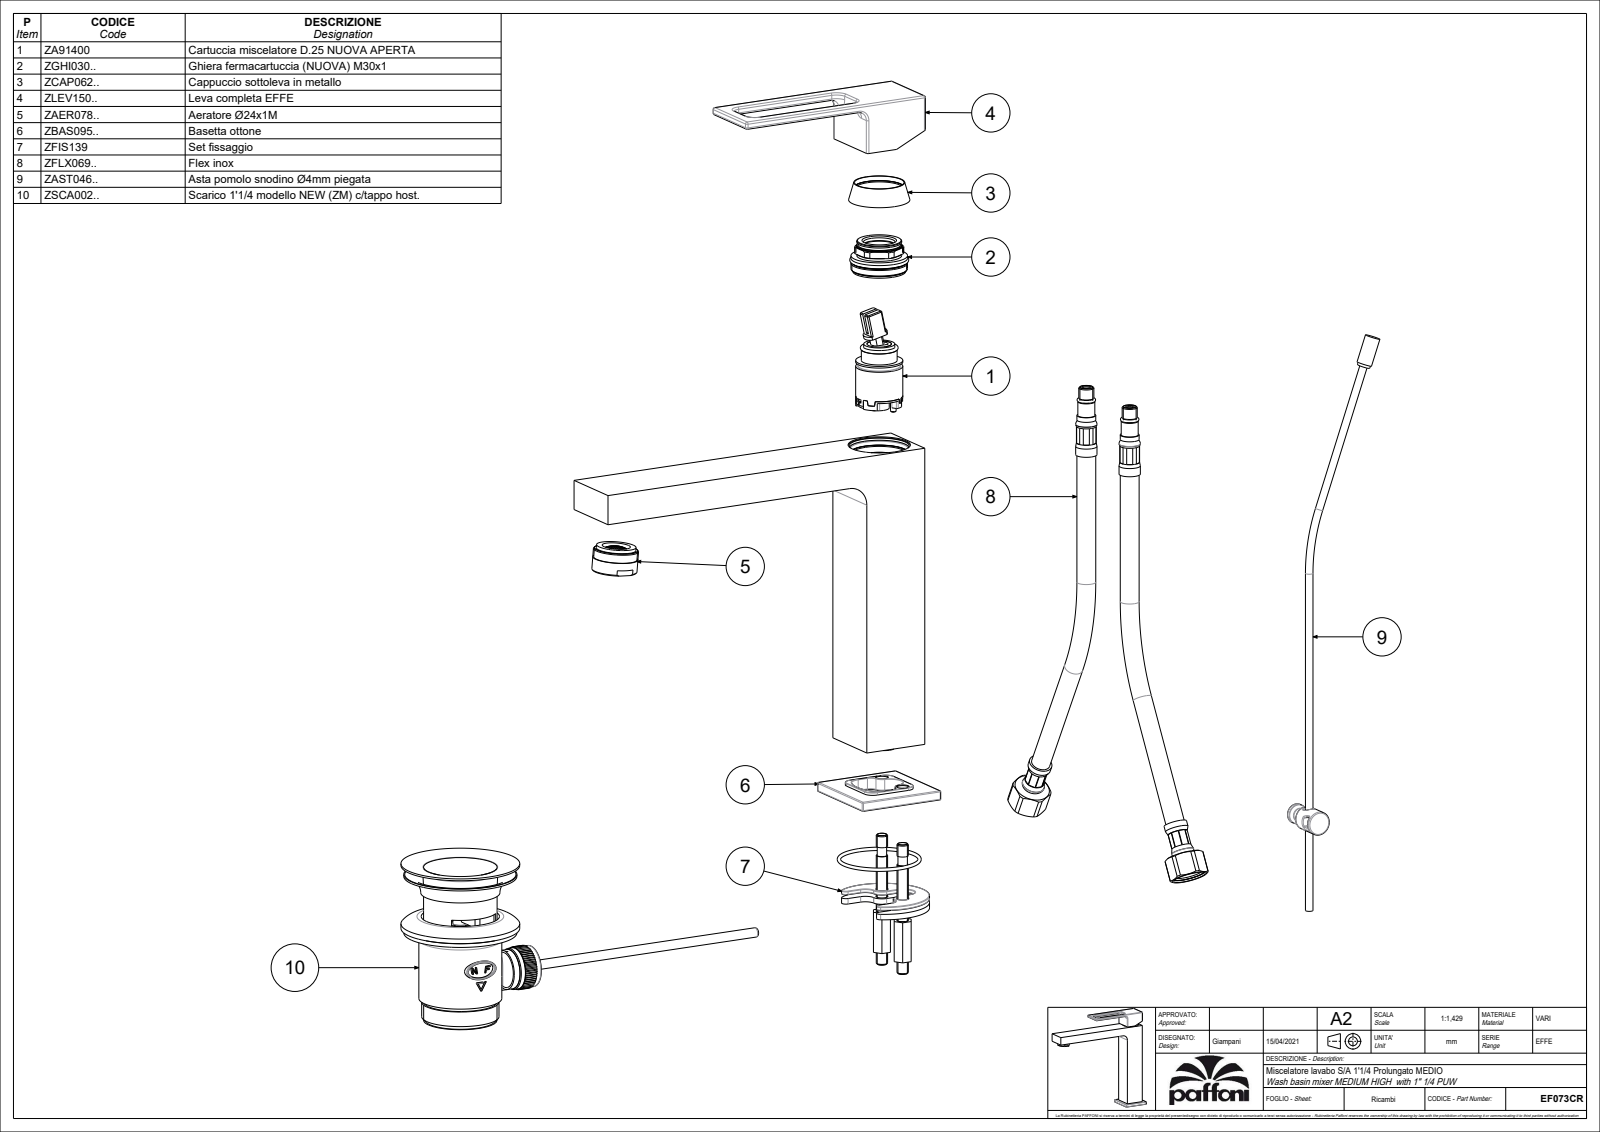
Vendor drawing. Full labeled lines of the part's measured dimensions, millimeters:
Part name (STEP PRODUCT): EF073CR
STEP written by: CREO PARAMETRIC BY PTC INC, 2020044 (CONFIG_CONTROL_DESIGN)
Units: millimetres
Bodies: 9 solids, 1946 faces (1555 planar, 225 cylindrical, 166 other)
Overall size (bounding box): 208.6 × 196.28 × 48
Volume: 151 912 mm³ · Surface area: 99 552 mm²
Round holes (diameter × count): ⌀5.5 ×3, ⌀4 ×2, ⌀6.2 ×2, ⌀3 ×1, ⌀4.2 ×1, ⌀4.5 ×1, ⌀5 ×1, ⌀7.8 ×1, ⌀16 ×1, ⌀17 ×1, ⌀20 ×1, ⌀21 ×1
Round bosses / shafts (diameter × count): ⌀8 ×3, ⌀8.9 ×2, ⌀6.5 ×2, ⌀41.8 ×1, ⌀24 ×1, ⌀19.5 ×1, ⌀18.8 ×1, ⌀16.8 ×1
Partial cylindrical surfaces — rounded edges, fillets, slot ends (radius × count): R1 ×66, R0.5 ×14, R5 ×9, R1.5 ×8, R0.25 ×6, R4 ×6, R3.5 ×2, R4.7 ×2
Main face-to-face distances: 3, 33, 36, 30, 13, 35.5, 16, 2.5, 32.5, 10
Hole centre spacings: 8.14, 11, 11.4, 13.6, 15.04, 17.87, 21.64, 22
